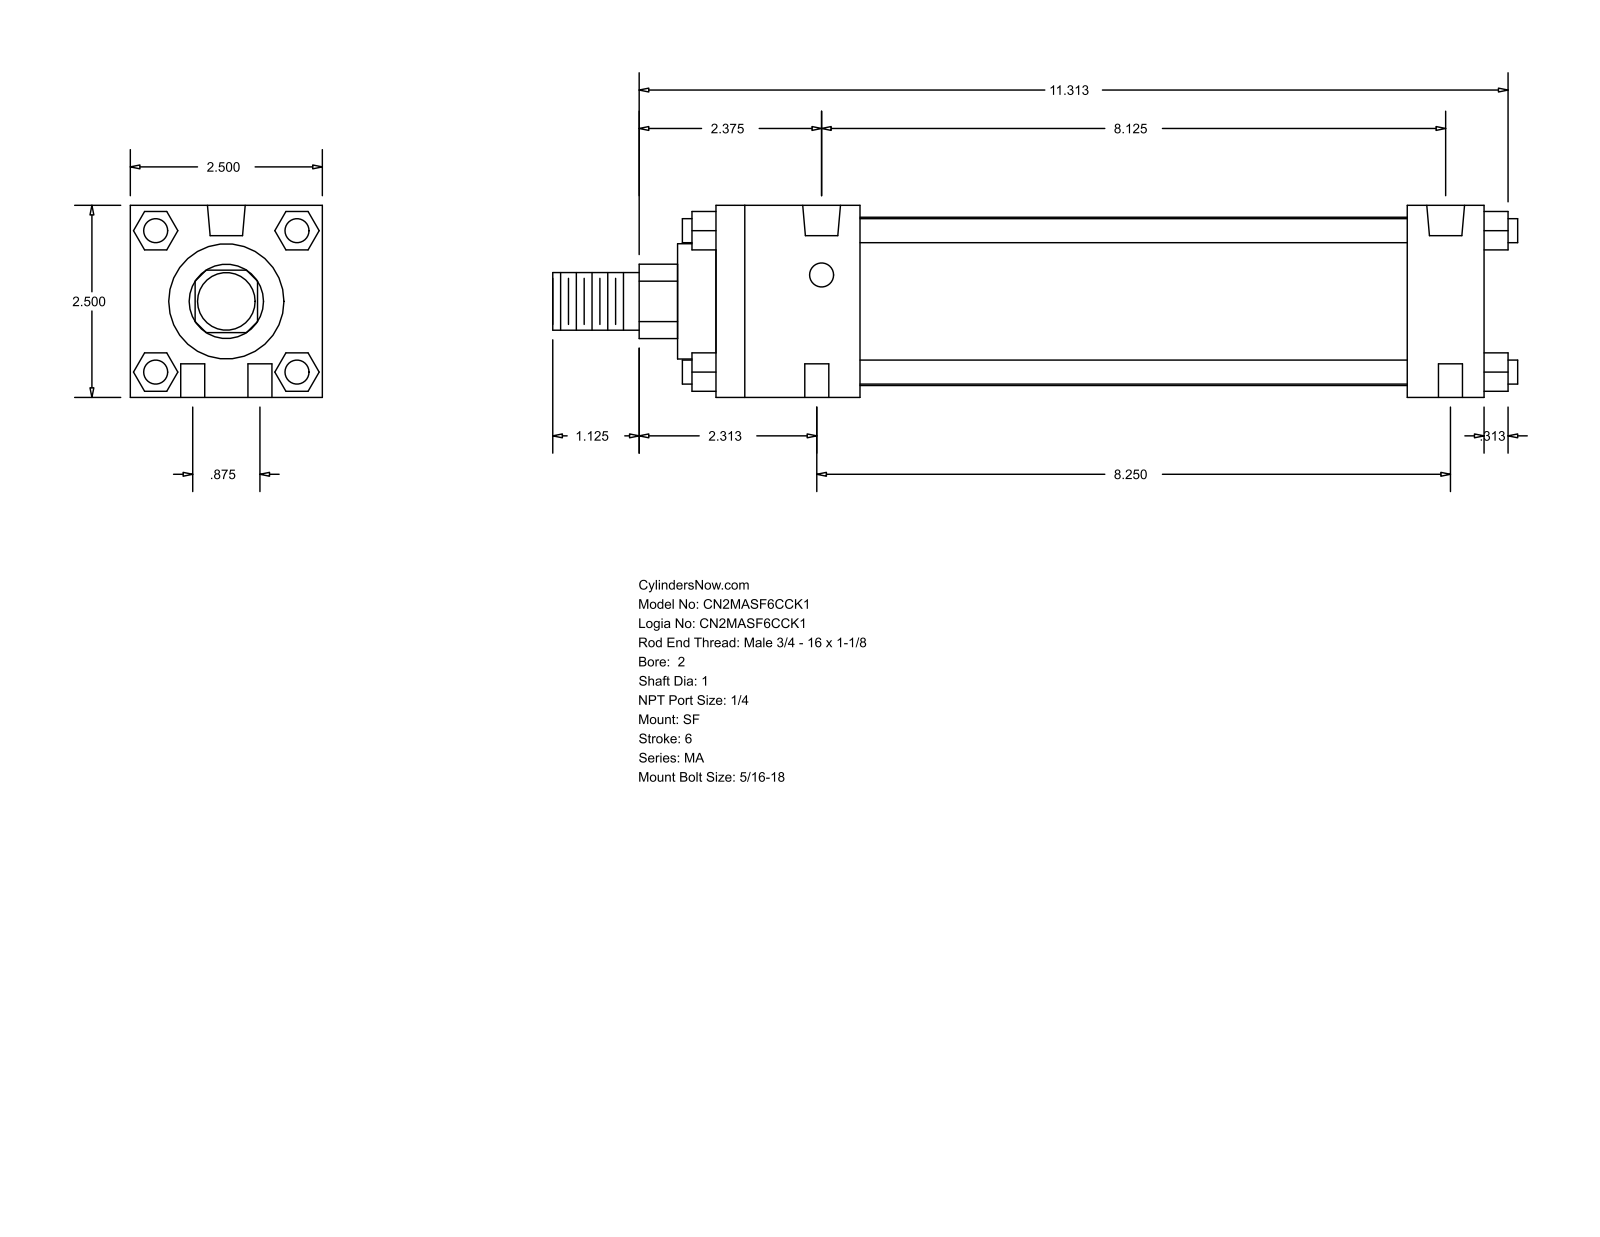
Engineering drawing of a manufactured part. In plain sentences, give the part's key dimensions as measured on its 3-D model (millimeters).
The part is named "MA_SF__0200_1". Its 3-D file was written by "GSSL Pune (CONFIG_CONTROL_DESIGN)". It is 0 solids with 124 faces: 94 planar, 30 cylindrical and 0 other. Overall it measures 319.09 by 63.5 by 63.5 millimeters. Round holes: 6 of diameter 7.94, 2 of diameter 12.49. Round bosses or shafts: 4 of diameter 7.94, 1 of diameter 55.63, 1 of diameter 38.1, 1 of diameter 25.4, 1 of diameter 19.05. Partial cylindrical surfaces (rounded edges, fillets, slot ends): 1 of radius 12.29. The main face-to-face distances are 63.5, 254, 12.7, 25.4, 228.6, 47.63, 180.97, 206.37, 40.47, 23.37. The hole center spacings are 11.22, 208.26, 22.22, 206.37, 209.55, 210.72.
